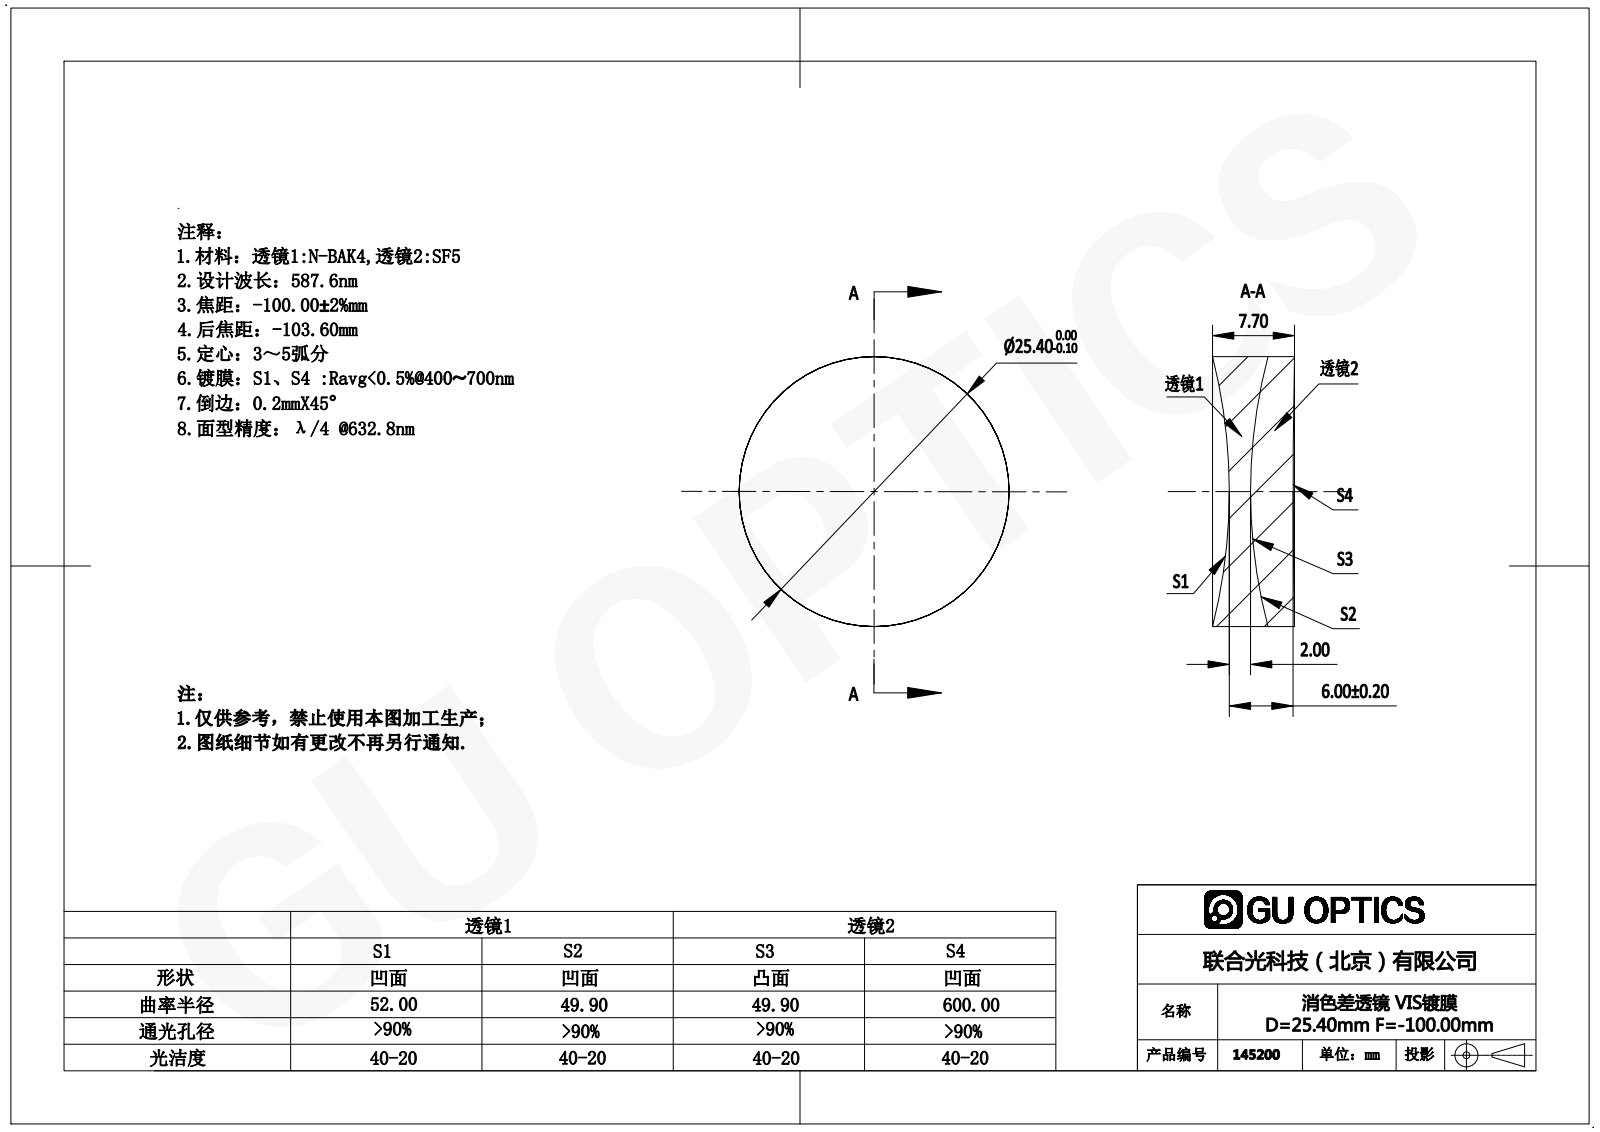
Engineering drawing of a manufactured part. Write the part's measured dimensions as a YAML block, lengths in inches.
part_name: "145200"
step_written_by: "SolidWorks 2016 (AUTOMOTIVE_DESIGN)"
units: inches
bodies: {solids: 2, faces: 12, planar: 0, cylindrical: 4, other: 8}
overall_size: [1, 1, 0.304]
volume: 0.212
surface_area: 4.134
round_bosses_or_shafts:
  - {diameter: 1, count: 1}
